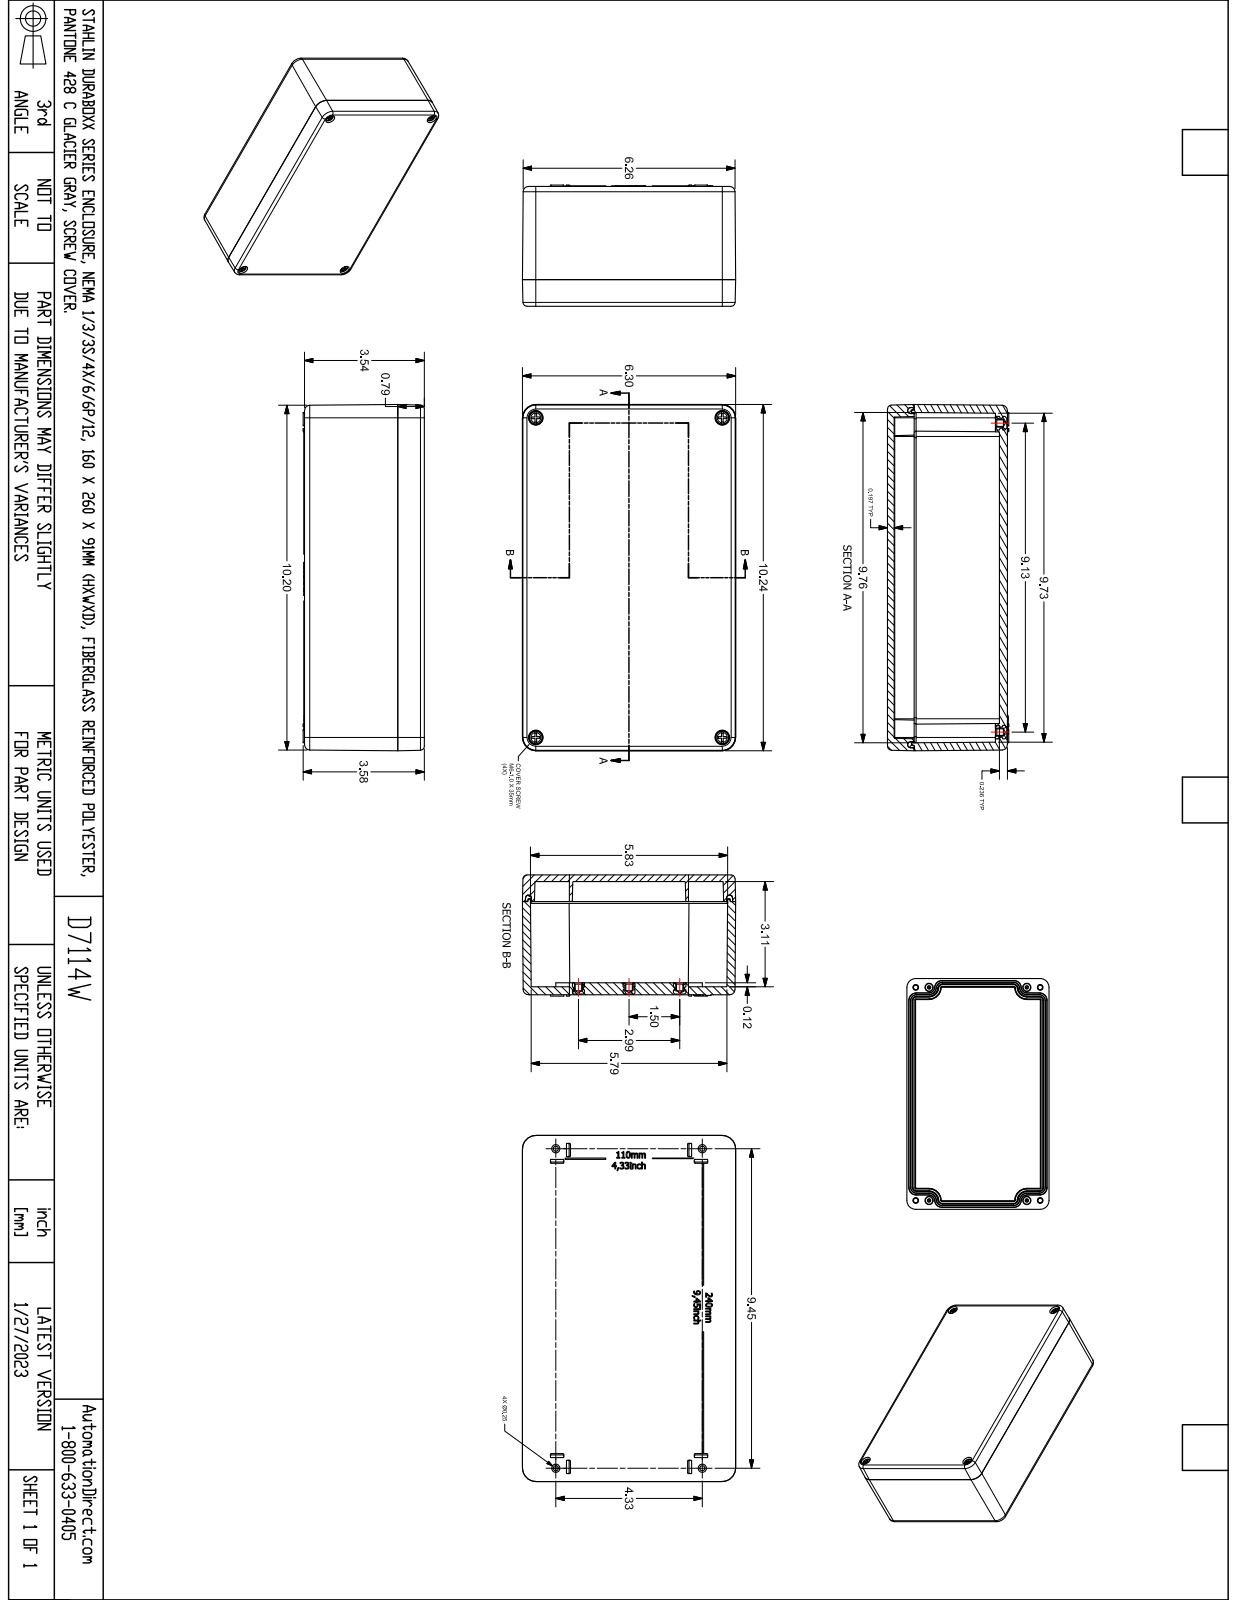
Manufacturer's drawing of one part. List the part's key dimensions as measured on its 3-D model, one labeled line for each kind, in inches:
Part name (STEP PRODUCT): DU7114W
STEP written by: SolidWorks 2018 (AUTOMOTIVE_DESIGN)
Units: inches
Bodies: 17 solids, 1266 faces (651 planar, 170 cylindrical, 445 other)
Overall size (bounding box): 10.236 × 6.299 × 3.583
Volume: 58.86 in³ · Surface area: 543 in²
Round holes (diameter × count): ⌀0.194 ×6, ⌀0.236 ×6, ⌀0.194 ×4, ⌀0.213 ×4, ⌀0.276 ×4
Round bosses / shafts (diameter × count): ⌀0.291 ×10, ⌀0.374 ×4, ⌀0.315 ×4, ⌀0.236 ×4, ⌀0.205 ×4
Partial cylindrical surfaces — rounded edges, fillets, slot ends (radius × count): R0.02 ×32, R0.089 ×12, R0.167 ×8, R0.344 ×8, R0.016 ×6, R0.118 ×4, R0.128 ×4, R0.128 ×4
Main face-to-face distances: 0.236, 3.543, 3.346, 0.197, 3.307, 3.11, 0.787, 2.756, 0.591, 2.52
Hole centre spacings: 1.27, 1.496, 2.76, 4.255, 9.256, 9.376, 9.691, 10.218
